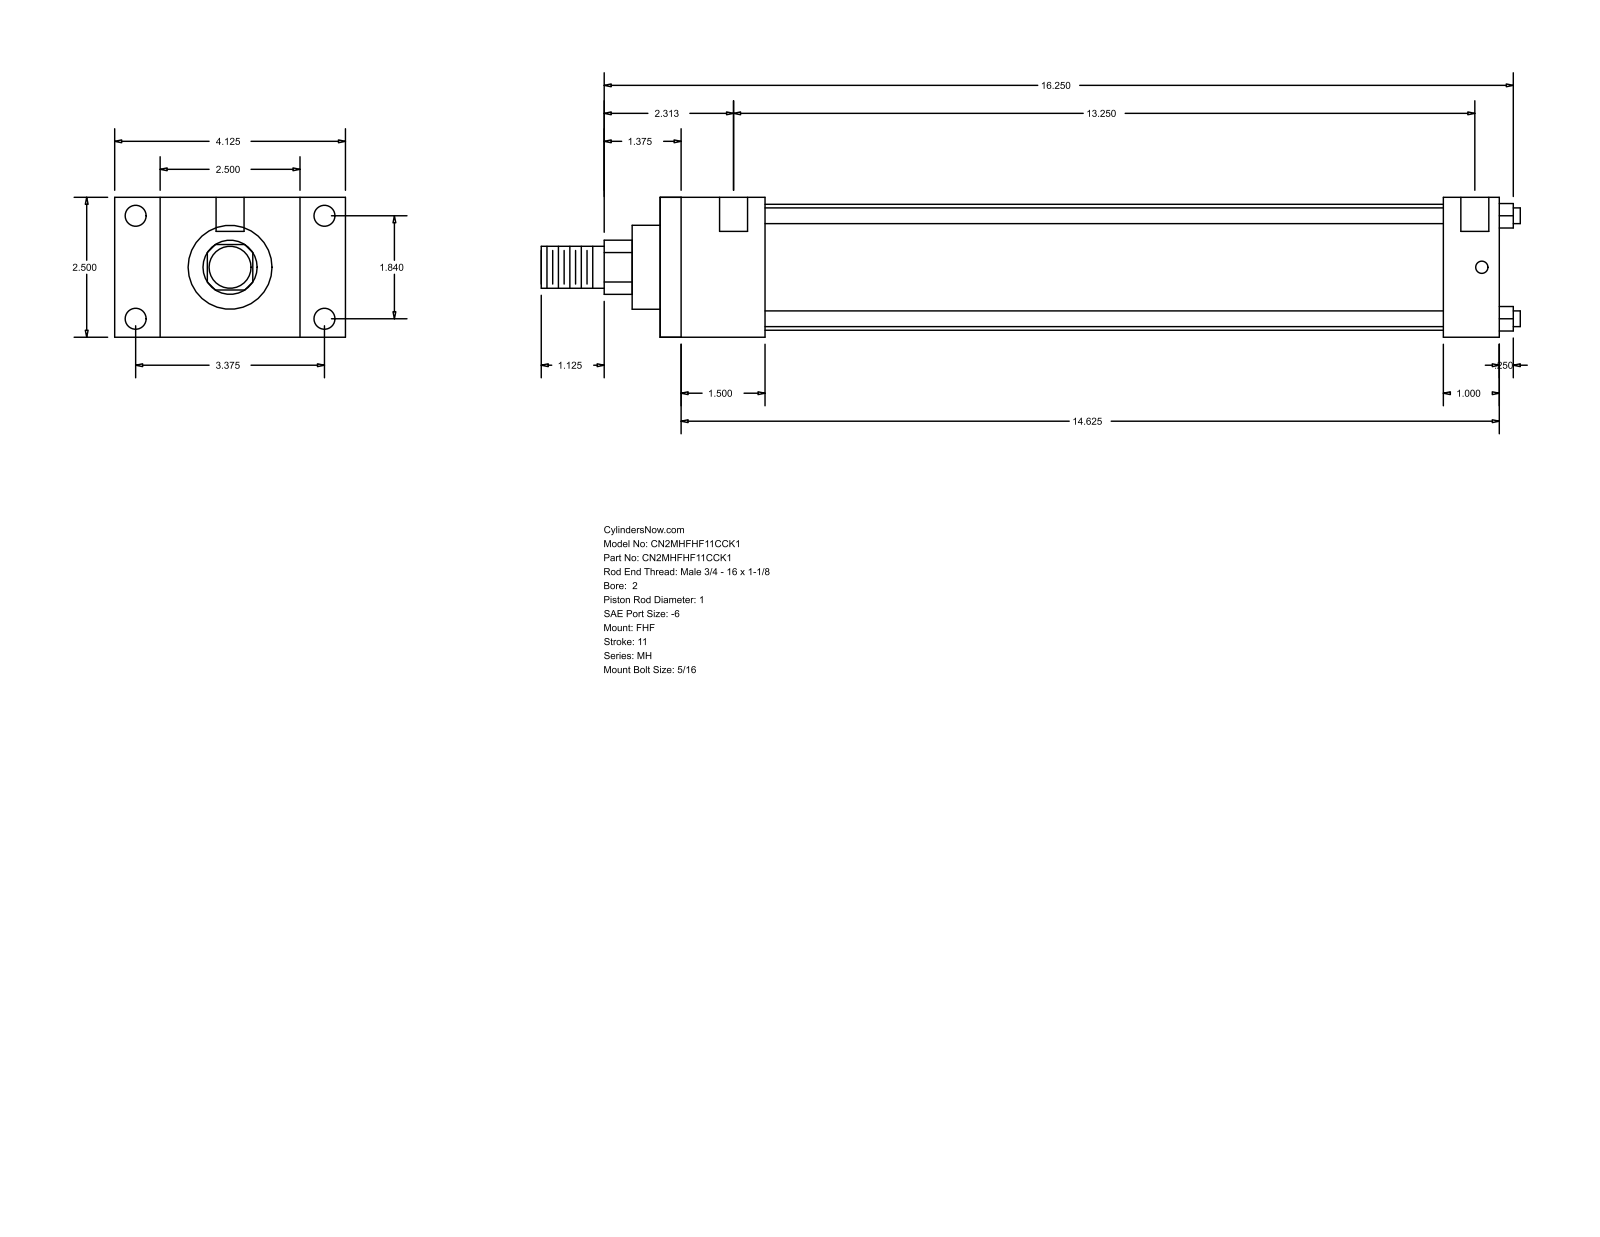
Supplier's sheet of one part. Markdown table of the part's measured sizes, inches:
| quantity | value |
| --- | --- |
| part name | MH_FHF__0200_1 |
| STEP written by | GSSL Pune (CONFIG_CONTROL_DESIGN) |
| units | inches |
| bodies | 0 solids, 88 faces (60 planar, 28 cylindrical, 0 other) |
| overall size | 17.5 × 4.125 × 2.5 |
| round holes (diameter × count) | 0.219 × 4, 0.375 × 4, 0.5 × 2 |
| round bosses / shafts (diameter × count) | 0.281 × 4, 2.25 × 1, 1.5 × 1, 1 × 1, 0.75 × 1 |
| partial cylindrical surfaces (radius × count) | 0.484 × 1 |
| main face-to-face distances | 2.5, 15, 1.875, 13.125, 0.813, 3.313, 4.125, 1, 14, 12.125 |
| hole center spacings | 1.84, 3.375, 3.844, 13.562, 0.125, 0.187, 13.25, 13.375 |
